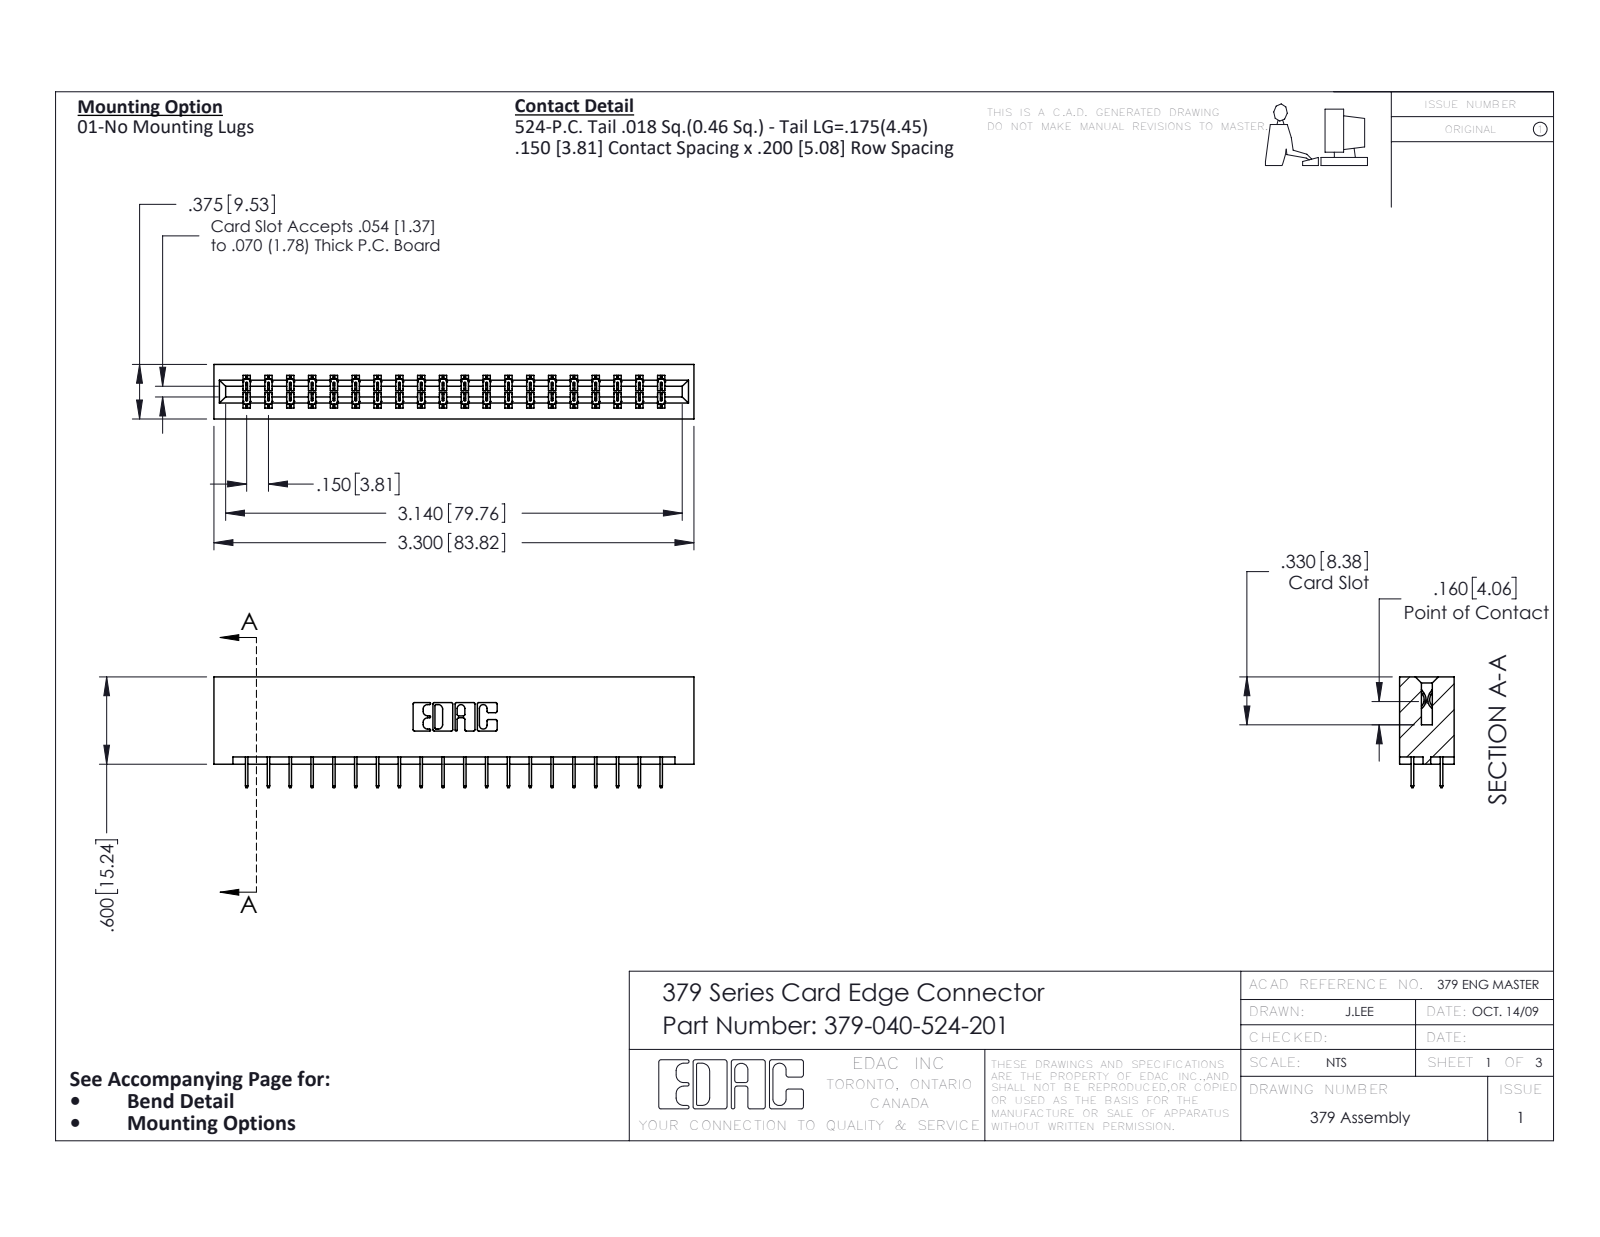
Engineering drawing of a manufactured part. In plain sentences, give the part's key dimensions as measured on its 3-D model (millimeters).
The part is named "345-292-001_345-293-124; 379 Part_Lugless; 379-040-524-201". Its 3-D file was written by "SolidWorks 2016 (CONFIG_CONTROL_DESIGN)". It is 41 solids with 2346 faces: 1746 planar, 600 cylindrical and 0 other. Overall it measures 83.8 by 19.4 by 9.5 millimeters. Its volume is 9 340 cubic millimeters and its surface area 10 140 square millimeters. Partial cylindrical surfaces (rounded edges, fillets, slot ends): 60 of radius 0.2, 22 of radius 0.3, 6 of radius 0.2, 6 of radius 0.8, 3 of radius 0.7, 2 of radius 0.4, 2 of radius 0.6, 2 of radius 0.6. The main face-to-face distances are 7.6, 1.9, 9.5, 5.1, 2.5, 3.8, 5.7, 14, 15.2, 1.3.
